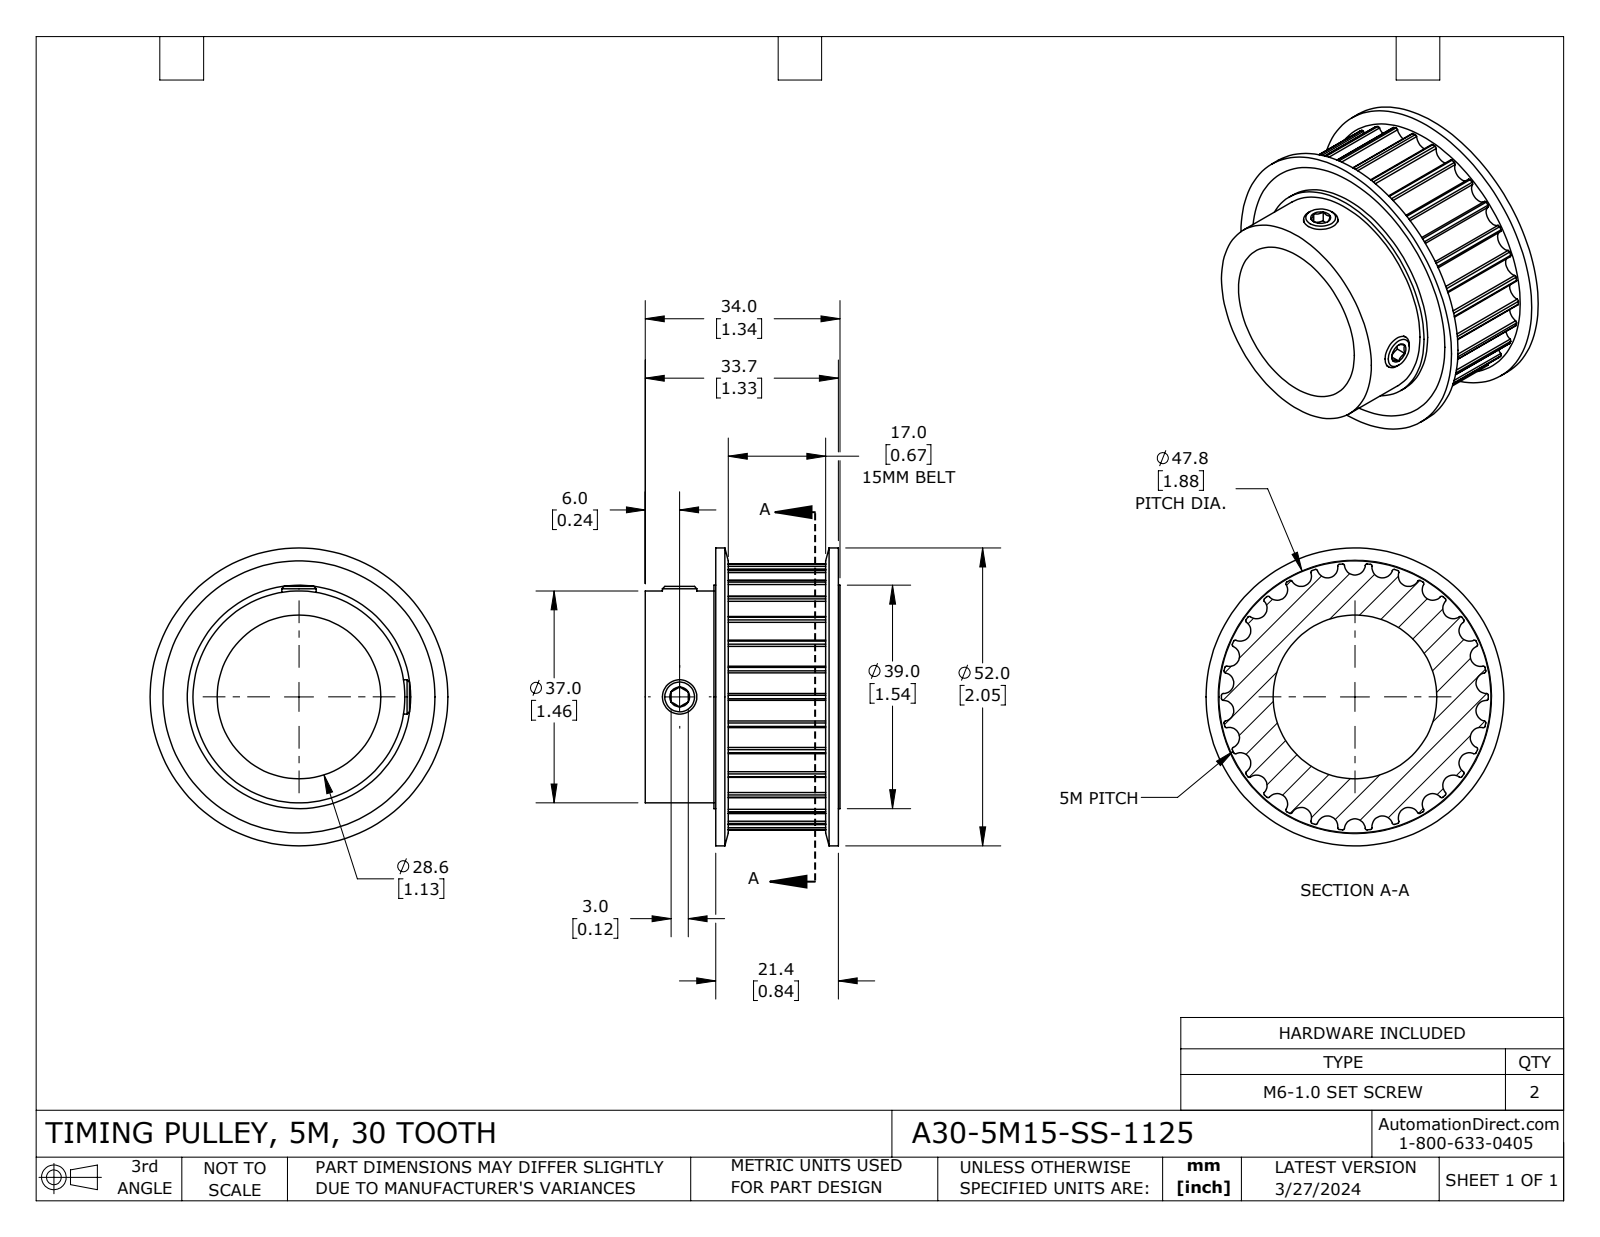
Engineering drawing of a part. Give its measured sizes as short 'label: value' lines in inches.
name: A30-5M15-SS-1125
written by: SolidWorks 2021 (CONFIG_CONTROL_DESIGN)
unit: in
bodies: 5 solids, 232 faces (25 planar, 173 cylindrical, 34 other)
size: 2.047 × 2.047 × 1.339
volume: 1.593 in³; area: 23.88 in²
holes: 2× ⌀0.197, 1× ⌀1.125, 1× ⌀1.535
bosses: 2× ⌀0.236, 1× ⌀2.047, 1× ⌀1.457
rounds: 60× R0.012, 30× R0.072, 1× R0.917
face distances: 0.063, 0.732, 0.669, 0.035, 0.098, 0.768, 0.831, 0.795, 1.339, 1.303
